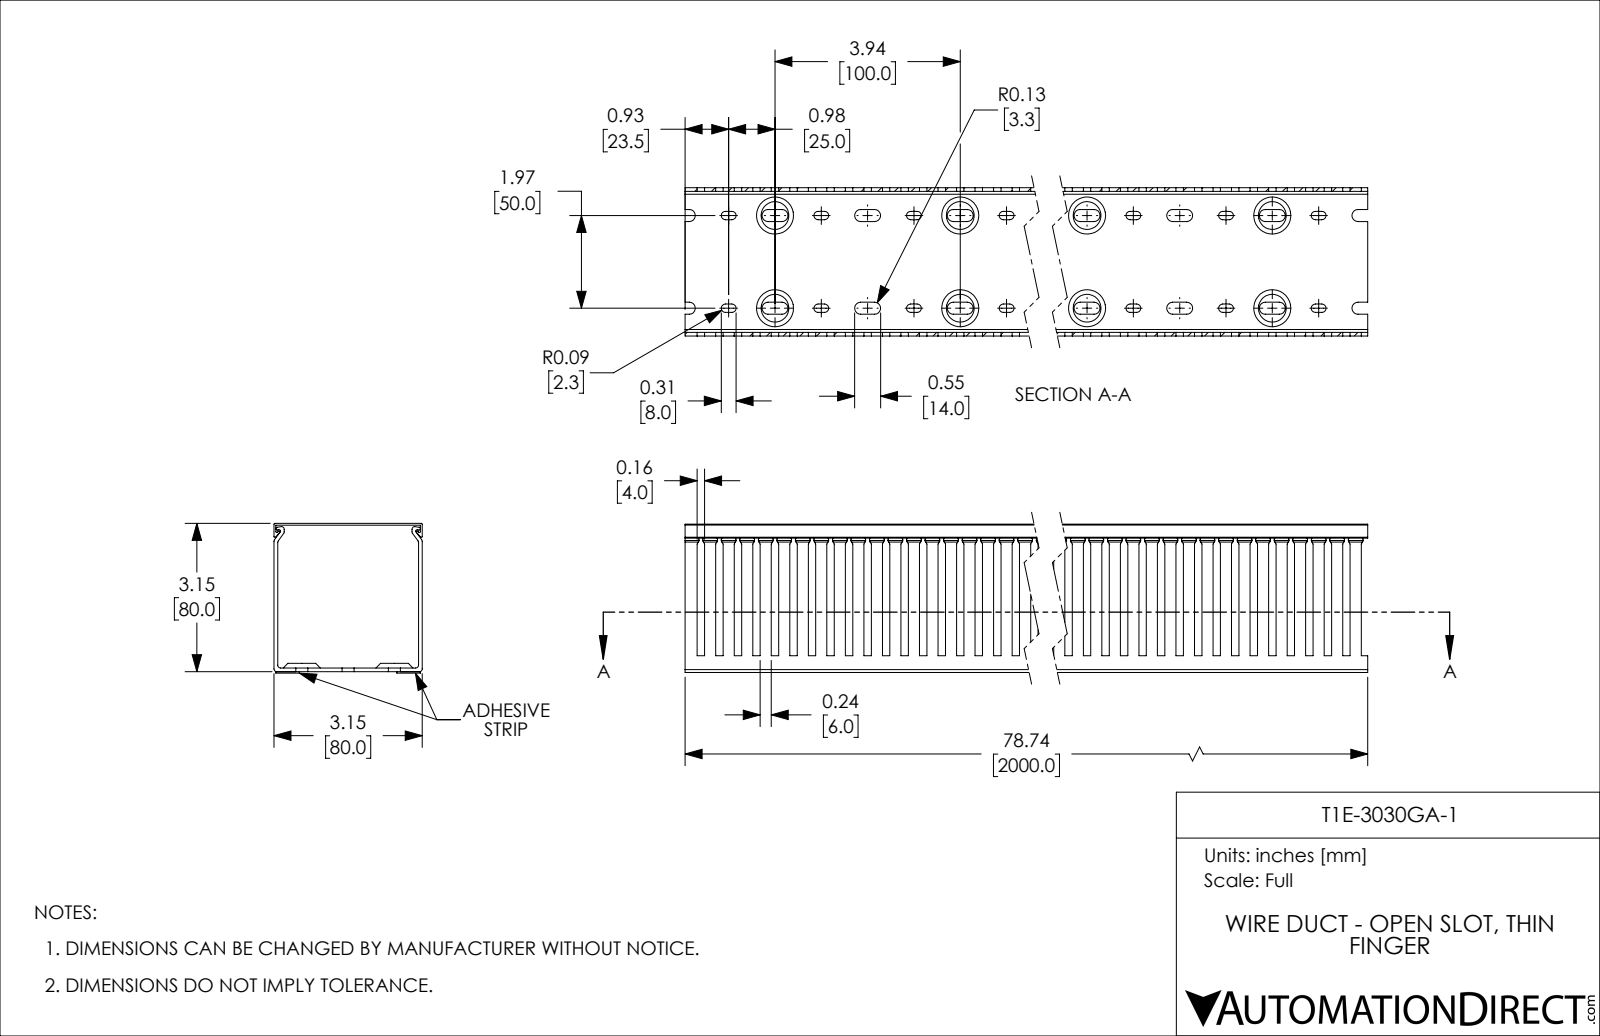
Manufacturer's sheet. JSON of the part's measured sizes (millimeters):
{"part_name": "T1E-3030GA-1", "step_written_by": "SolidWorks 2021 (CONFIG_CONTROL_DESIGN)", "units": "millimeters", "bodies": {"solids": 4, "faces": 1585, "planar": 774, "cylindrical": 731, "other": 80}, "overall_size": [2000, 80.79, 80], "volume_mm3": 1174000, "surface_area_mm2": 1442000, "partial_cylinders_radius": [[3.25, 200], [2.25, 160], [1.5, 12], [0.5, 8], [0.75, 6]], "face_to_face_distances": [2, 78, 80, 1, 79, 77, 76, 0.79, 2.79, 79.79]}
